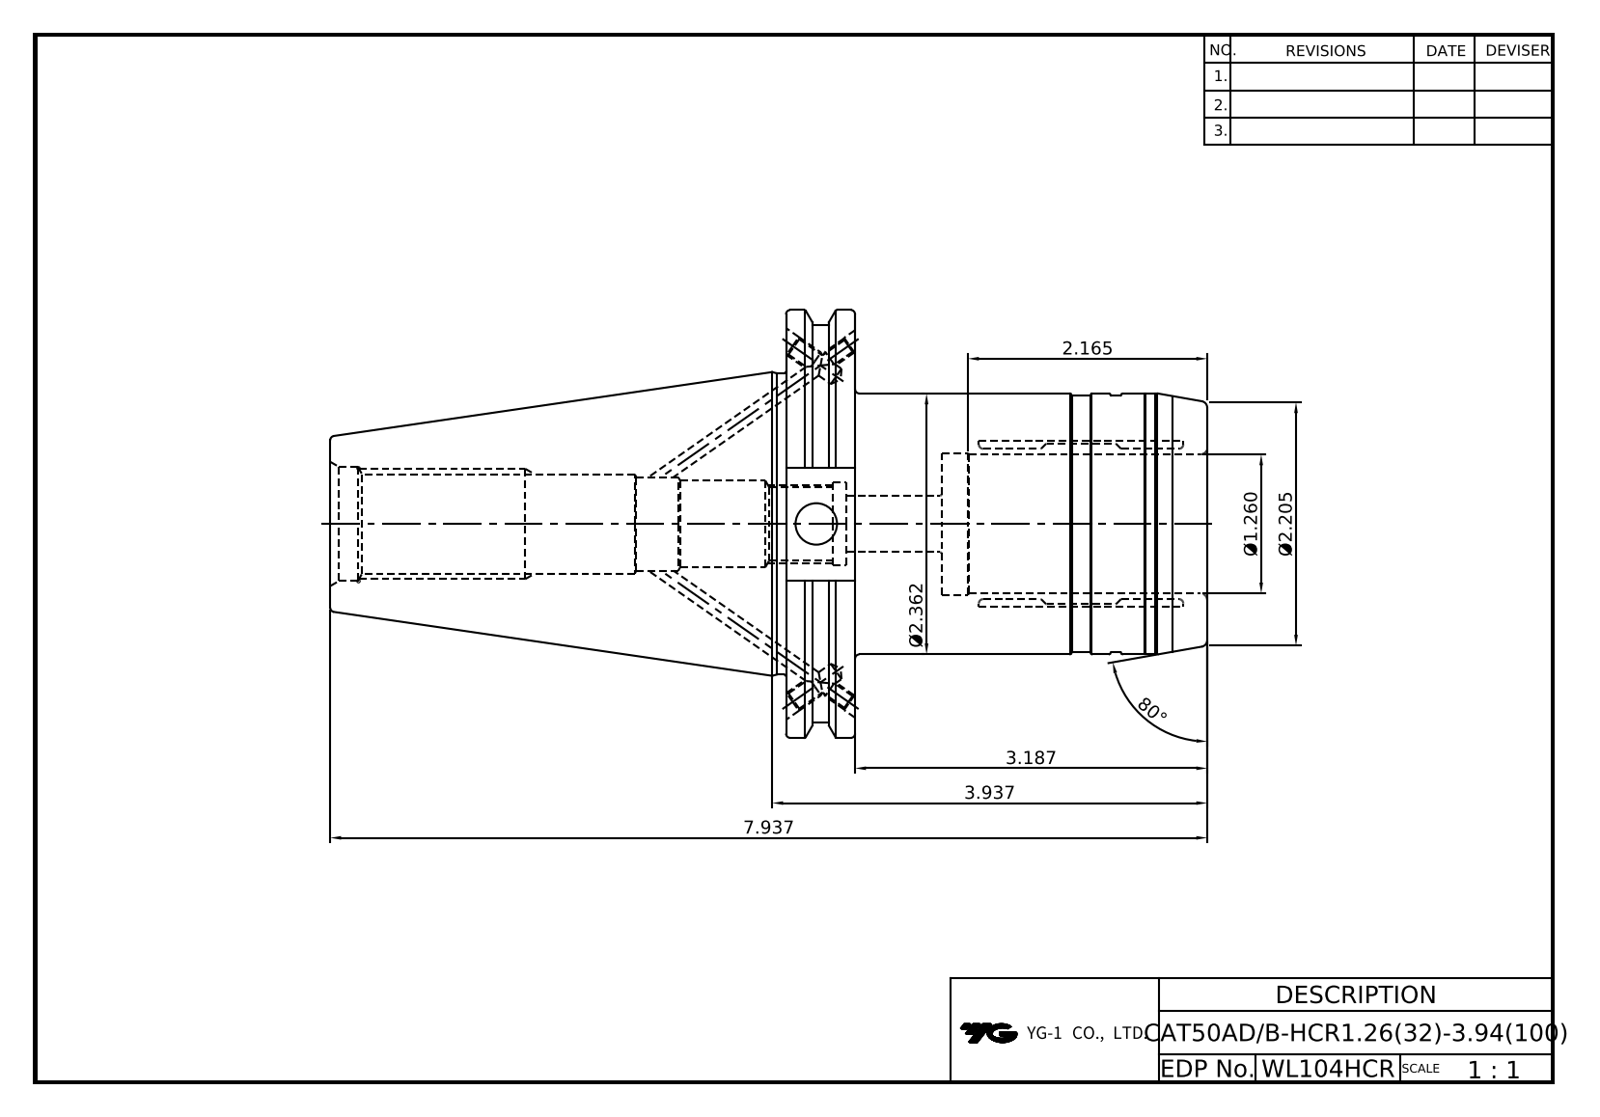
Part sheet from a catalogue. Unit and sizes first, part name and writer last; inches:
Units: inches
Overall size (bounding box): 7.937 × 3.875 × 3.728
Round holes (diameter × count): ⌀0.163 ×4, ⌀0.197 ×4, ⌀0.375 ×1, ⌀0.52 ×1, ⌀0.666 ×1, ⌀0.748 ×1, ⌀0.865 ×1, ⌀1.031 ×1, ⌀1.26 ×1, ⌀1.276 ×1
Round bosses / shafts (diameter × count): ⌀3.875 ×1, ⌀3.594 ×1, ⌀2.726 ×1, ⌀2.362 ×1, ⌀2.323 ×1
Main face-to-face distances: 0.625, 3.812, 3.187, 1.415, 0.789, 2.398, 4.125, 4.75, 5.539, 7.937
Hole centre spacings: 2.35
Volume: 30.09 in³ · Surface area: 104 in²
Bodies: 1 solid, 100 faces (35 planar, 32 cylindrical, 33 other)
Part name (STEP PRODUCT): LO-CAT50ADB-HCR32-100
STEP written by: Autodesk Inventor 2025 (AUTOMOTIVE_DESIGN)
